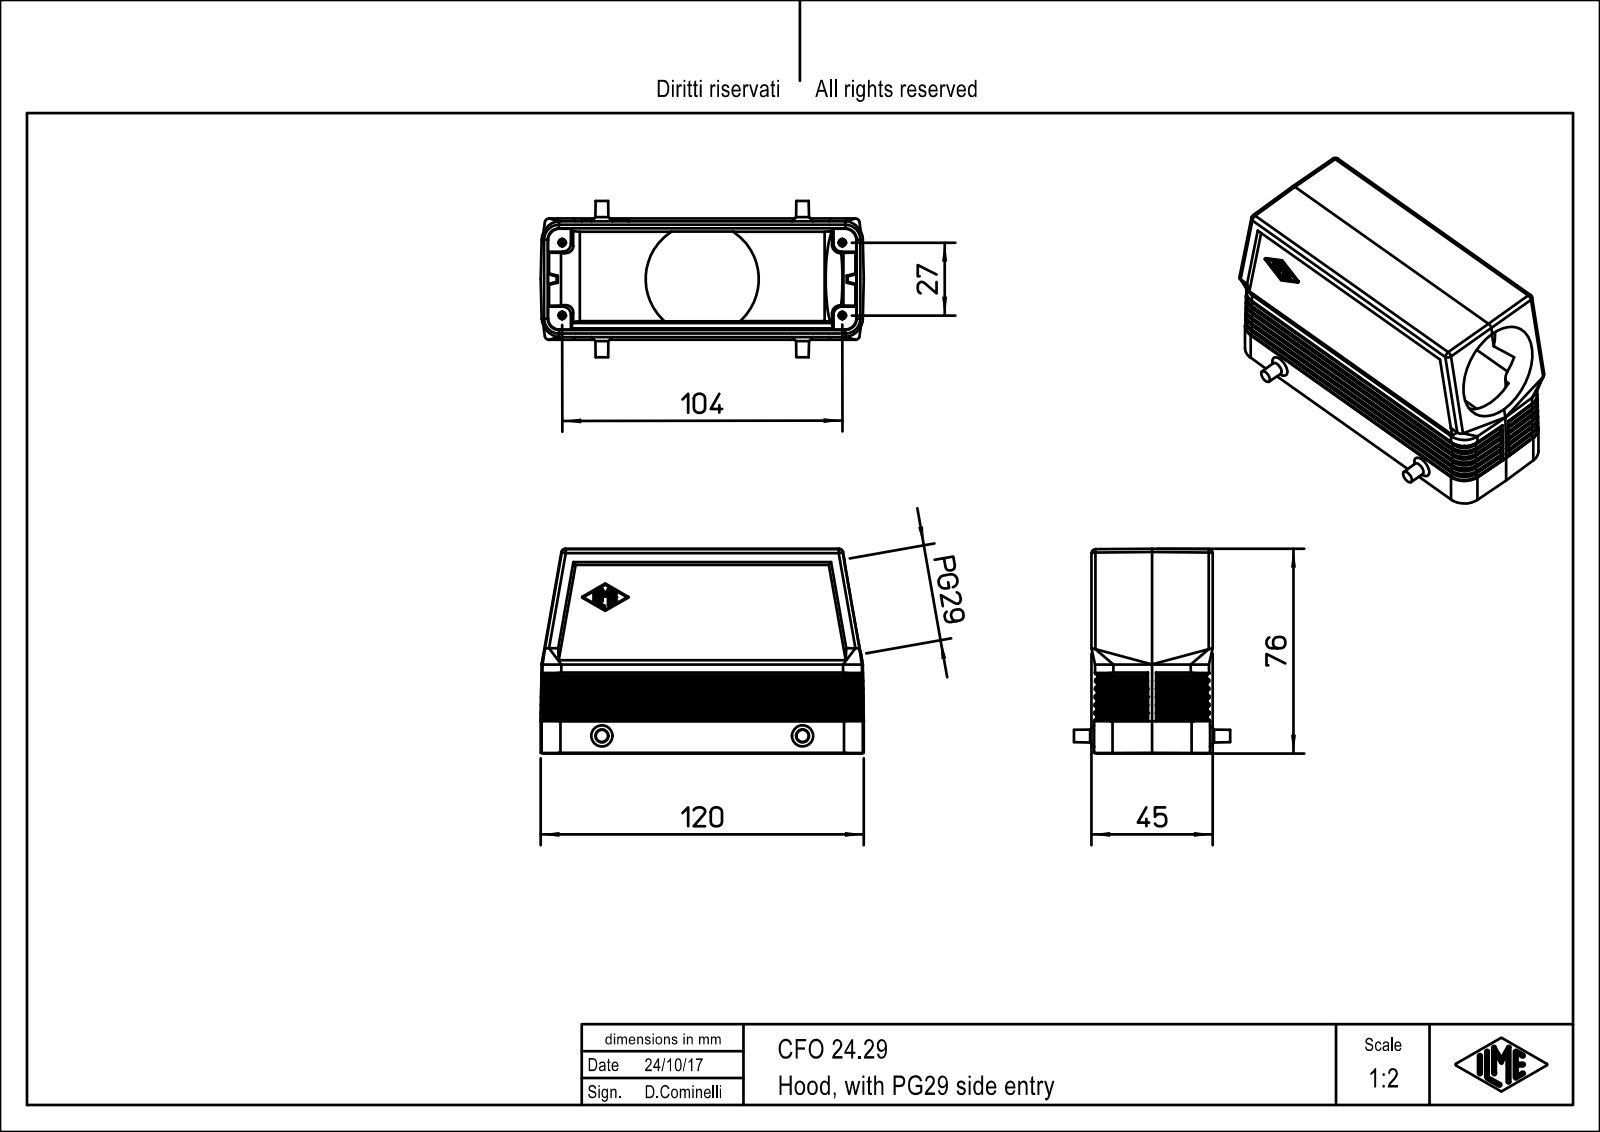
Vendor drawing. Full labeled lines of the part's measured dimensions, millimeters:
Part name (STEP PRODUCT): CFO_24.29
STEP written by: PTC Creo Elements/Direct Modeling 19.0E 27-Jun-2016 (C) Parametric Technology GmbH (AUTOMOTIVE_DESIGN)
Units: millimetres
Bodies: 1 solid, 527 faces (240 planar, 135 cylindrical, 152 other)
Overall size (bounding box): 120 × 76 × 58
Volume: 103 755 mm³ · Surface area: 53 837 mm²
Round holes (diameter × count): ⌀35.7 ×1
Partial cylindrical surfaces — rounded edges, fillets, slot ends (radius × count): R0.5 ×78, R0.33 ×15, R1.5 ×10, R7 ×8, R3 ×4, R4.2 ×4, R0.17 ×3, R0.67 ×1
Main face-to-face distances: 43, 2.01, 2, 4, 3.2, 1, 44, 6, 8.45, 6.01
